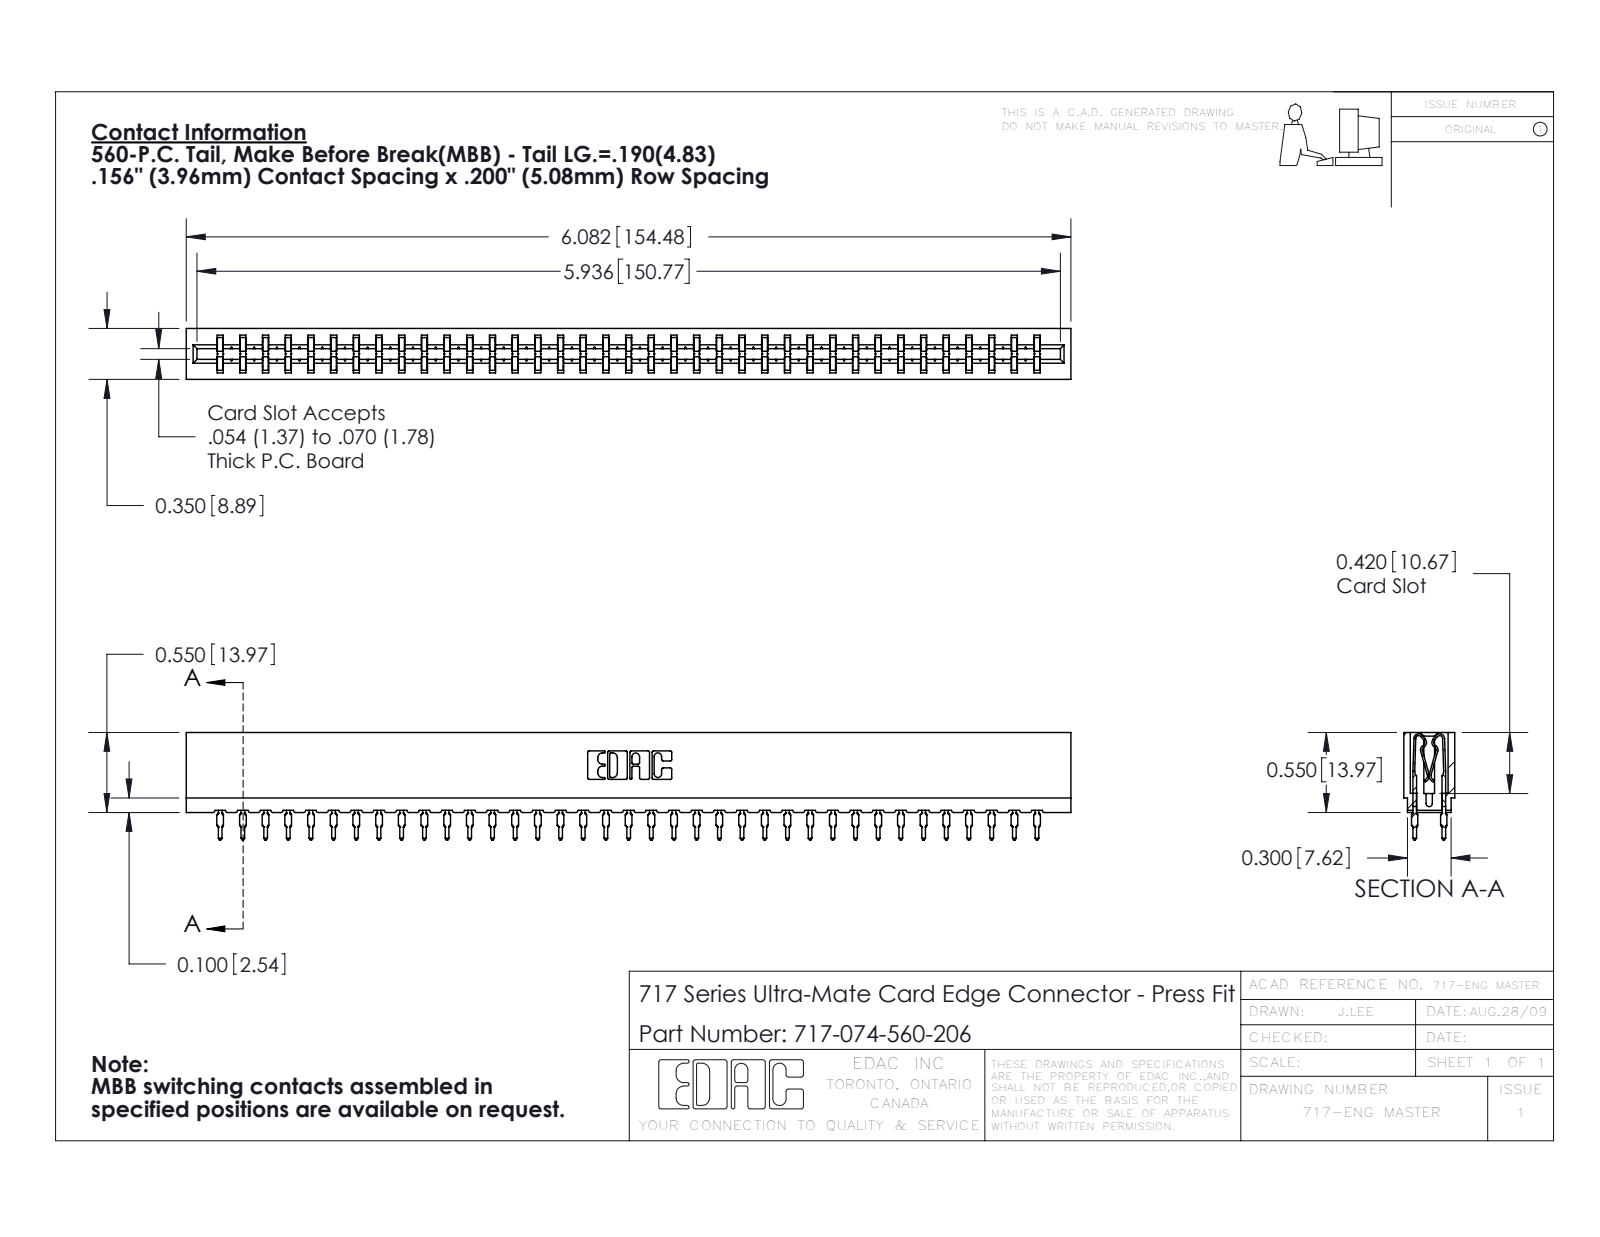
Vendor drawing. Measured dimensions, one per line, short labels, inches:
name: 717 Part_Insulator Option - 06; 745-292-001_560; 717-074-560-206
written by: SolidWorks 2016 (CONFIG_CONTROL_DESIGN)
unit: in
bodies: 75 solids, 7420 faces (3865 planar, 1631 cylindrical, 1924 other)
size: 6.082 × 0.739 × 0.35
volume: 0.835 in³; area: 34.35 in²
rounds: 148× R0.021, 74× R0.015, 22× R0.01, 8× R0.005, 8× R0.011, 6× R0.007, 6× R0.031, 3× R0.026
face distances: 0.212, 0.138, 0.35, 0.063, 0.287, 0.076, 0.149, 0.074, 0.045, 0.305
